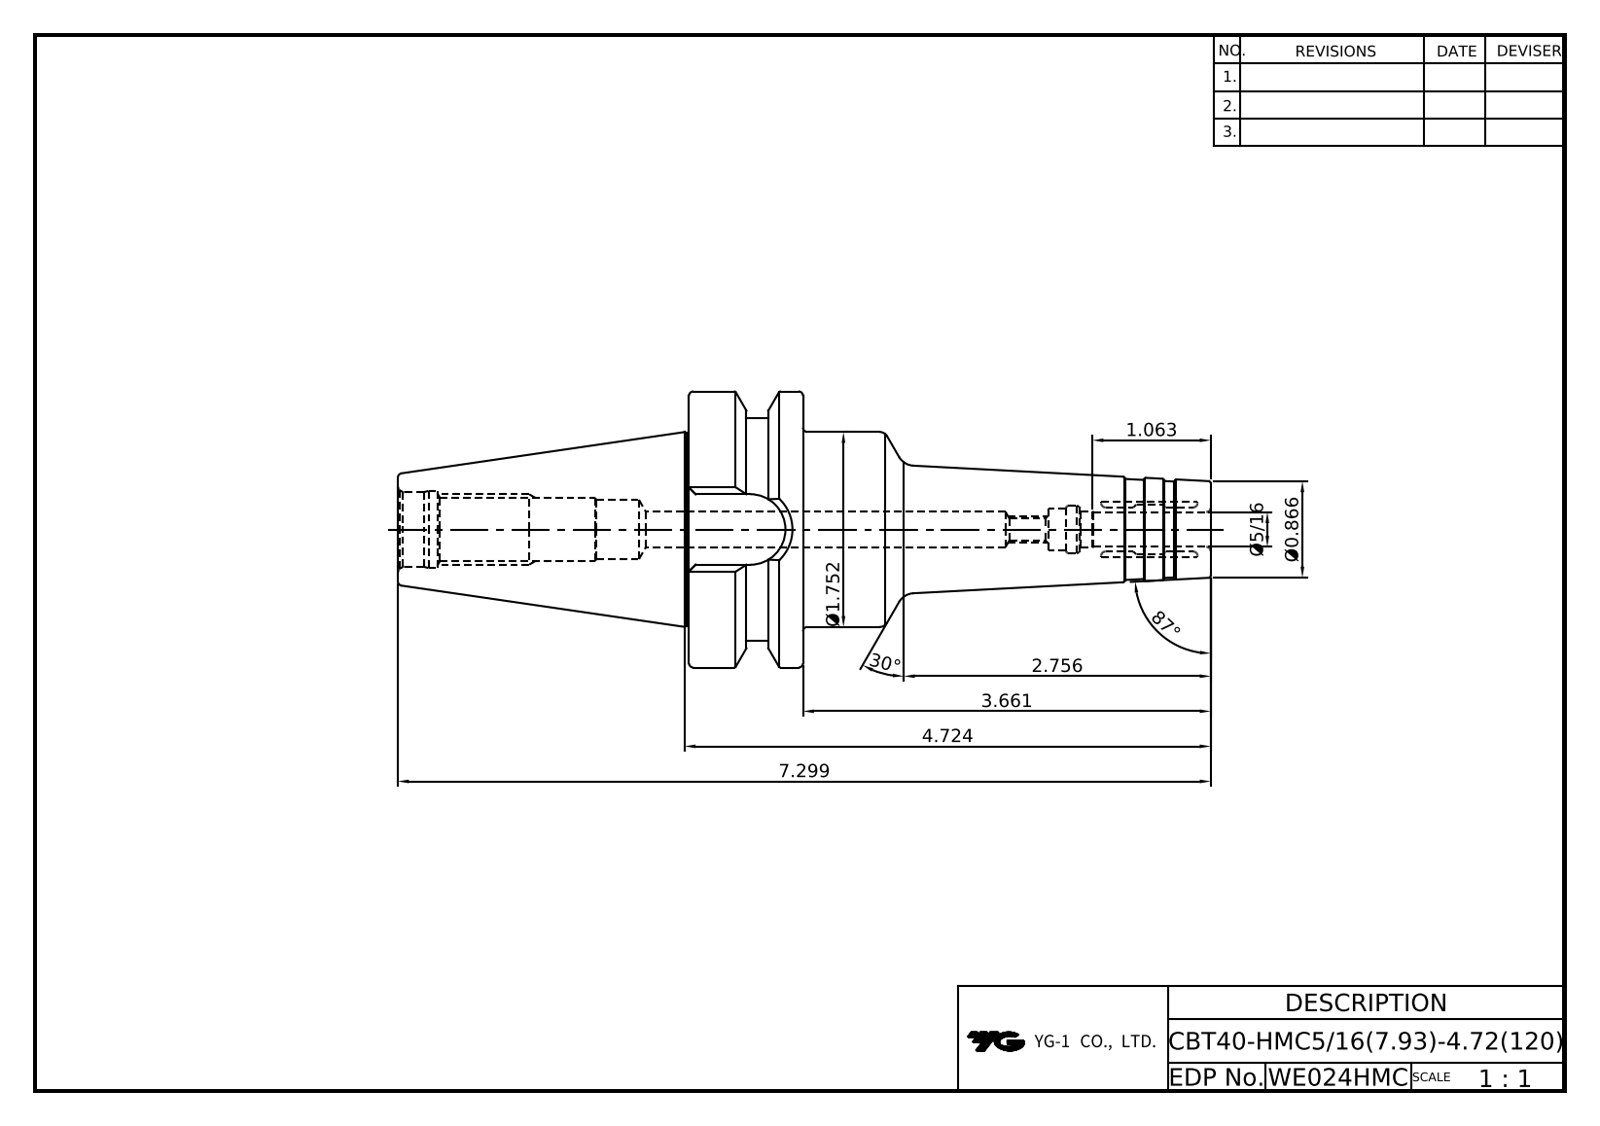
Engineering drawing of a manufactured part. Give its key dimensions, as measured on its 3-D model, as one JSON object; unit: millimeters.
{"part_name": "LO-CBT40-HMC7.9375-120", "step_written_by": "Autodesk Inventor 2022 (AUTOMOTIVE_DESIGN)", "units": "millimeters", "bodies": {"solids": 1, "faces": 83, "planar": 24, "cylindrical": 17, "other": 42}, "overall_size": [185.4, 63, 63], "volume_mm3": 187617, "surface_area_mm2": 32760, "round_holes": [[4.92, 1], [7.94, 1], [8, 1], [8.54, 1], [13.5, 1], [13.84, 1], [17, 1], [17.6, 1]], "round_bosses_or_shafts": [[63, 1], [51, 1], [44.5, 1], [44, 1]], "partial_cylinders_radius": [[8.05, 1]], "face_to_face_distances": [26, 45.2, 119, 93, 18.1, 7.9, 100.9, 13.1, 5, 12.9]}
